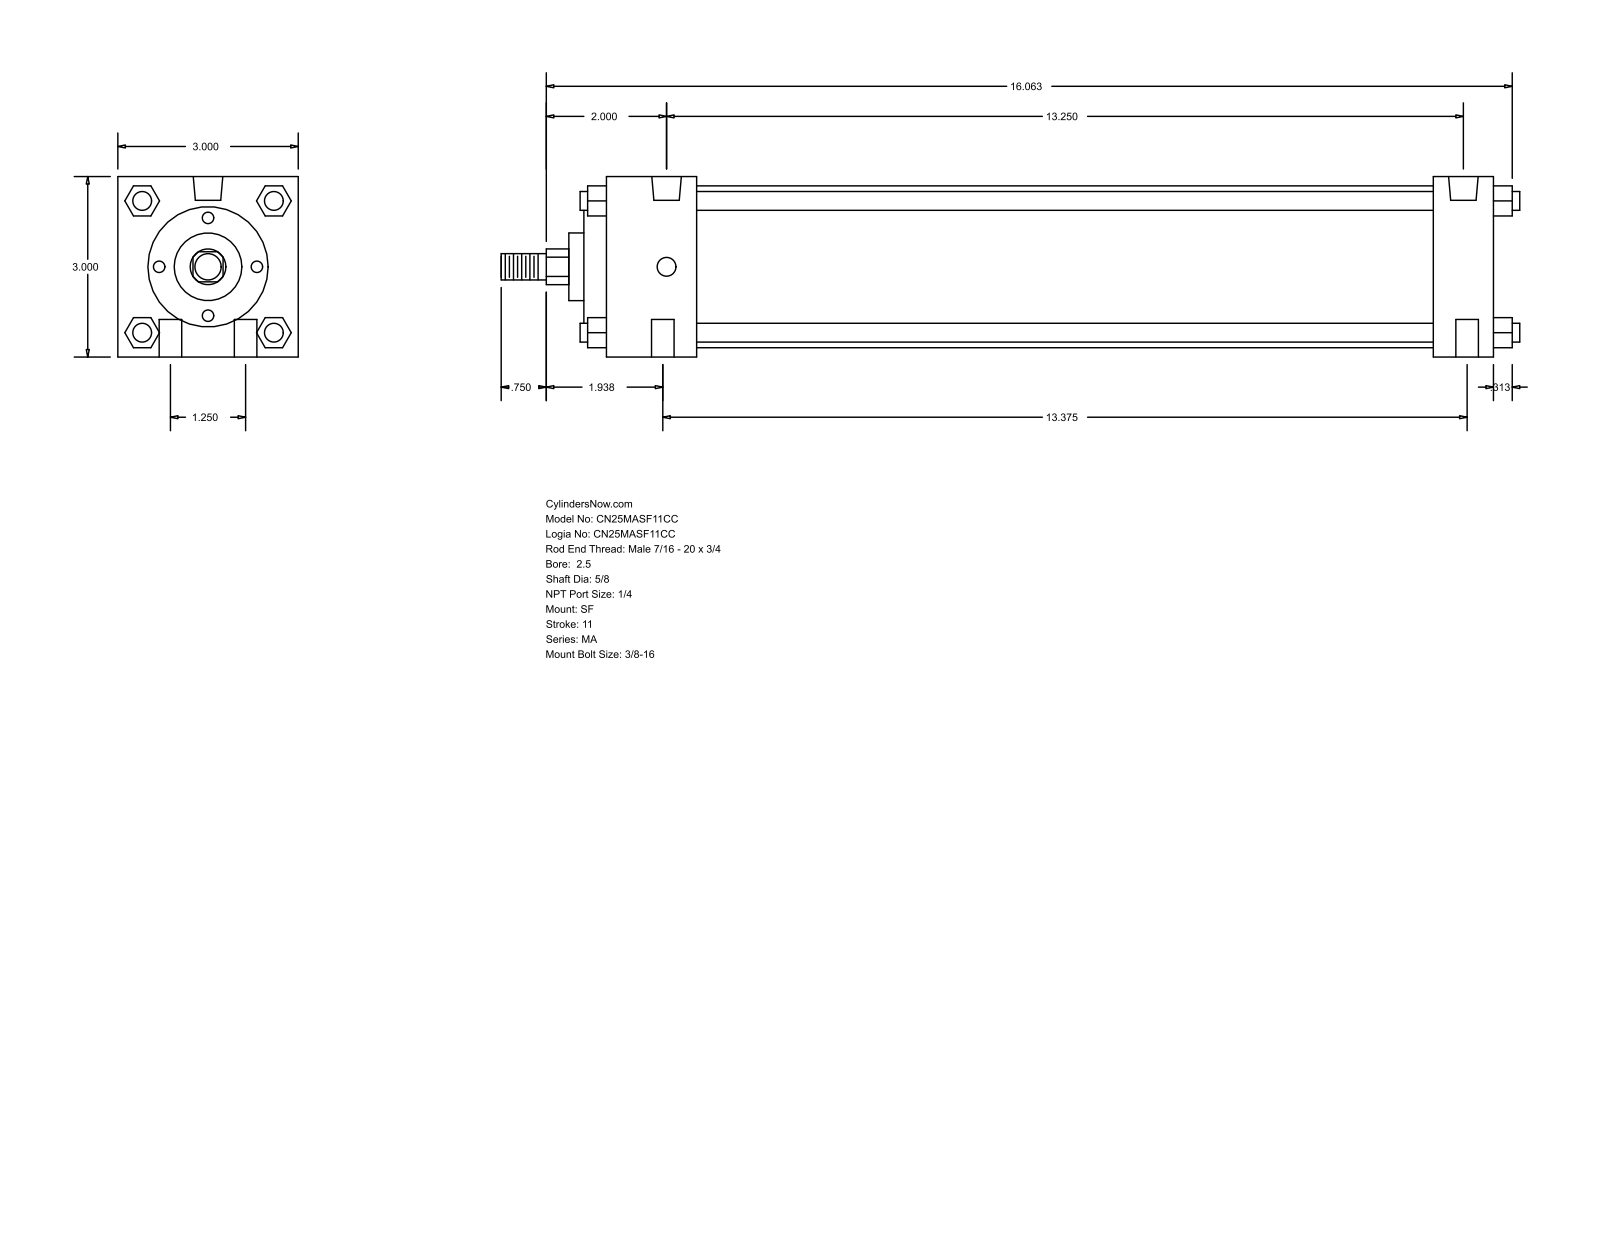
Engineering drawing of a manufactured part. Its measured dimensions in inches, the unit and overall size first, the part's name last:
Units: inches
Overall size (bounding box): 16.937 × 3 × 3
Round holes (diameter × count): ⌀0.375 ×4, ⌀0.313 ×2, ⌀0.492 ×2
Round bosses / shafts (diameter × count): ⌀0.313 ×4, ⌀2.69 ×1, ⌀2 ×1, ⌀1.125 ×1, ⌀0.625 ×1, ⌀0.437 ×1
Partial cylindrical surfaces — rounded edges, fillets, slot ends (radius × count): R0.297 ×1
Main face-to-face distances: 3, 14.75, 1, 13.75, 1.5, 12.25, 13.25, 0.5, 0.375, 1.875
Hole centre spacings: 0.628, 13.327, 1.25, 13.25, 13.375, 13.433
Bodies: 0 solids, 126 faces (95 planar, 31 cylindrical, 0 other)
Part name (STEP PRODUCT): MA_SF__0250_0.625
STEP written by: GSSL Pune (CONFIG_CONTROL_DESIGN)
